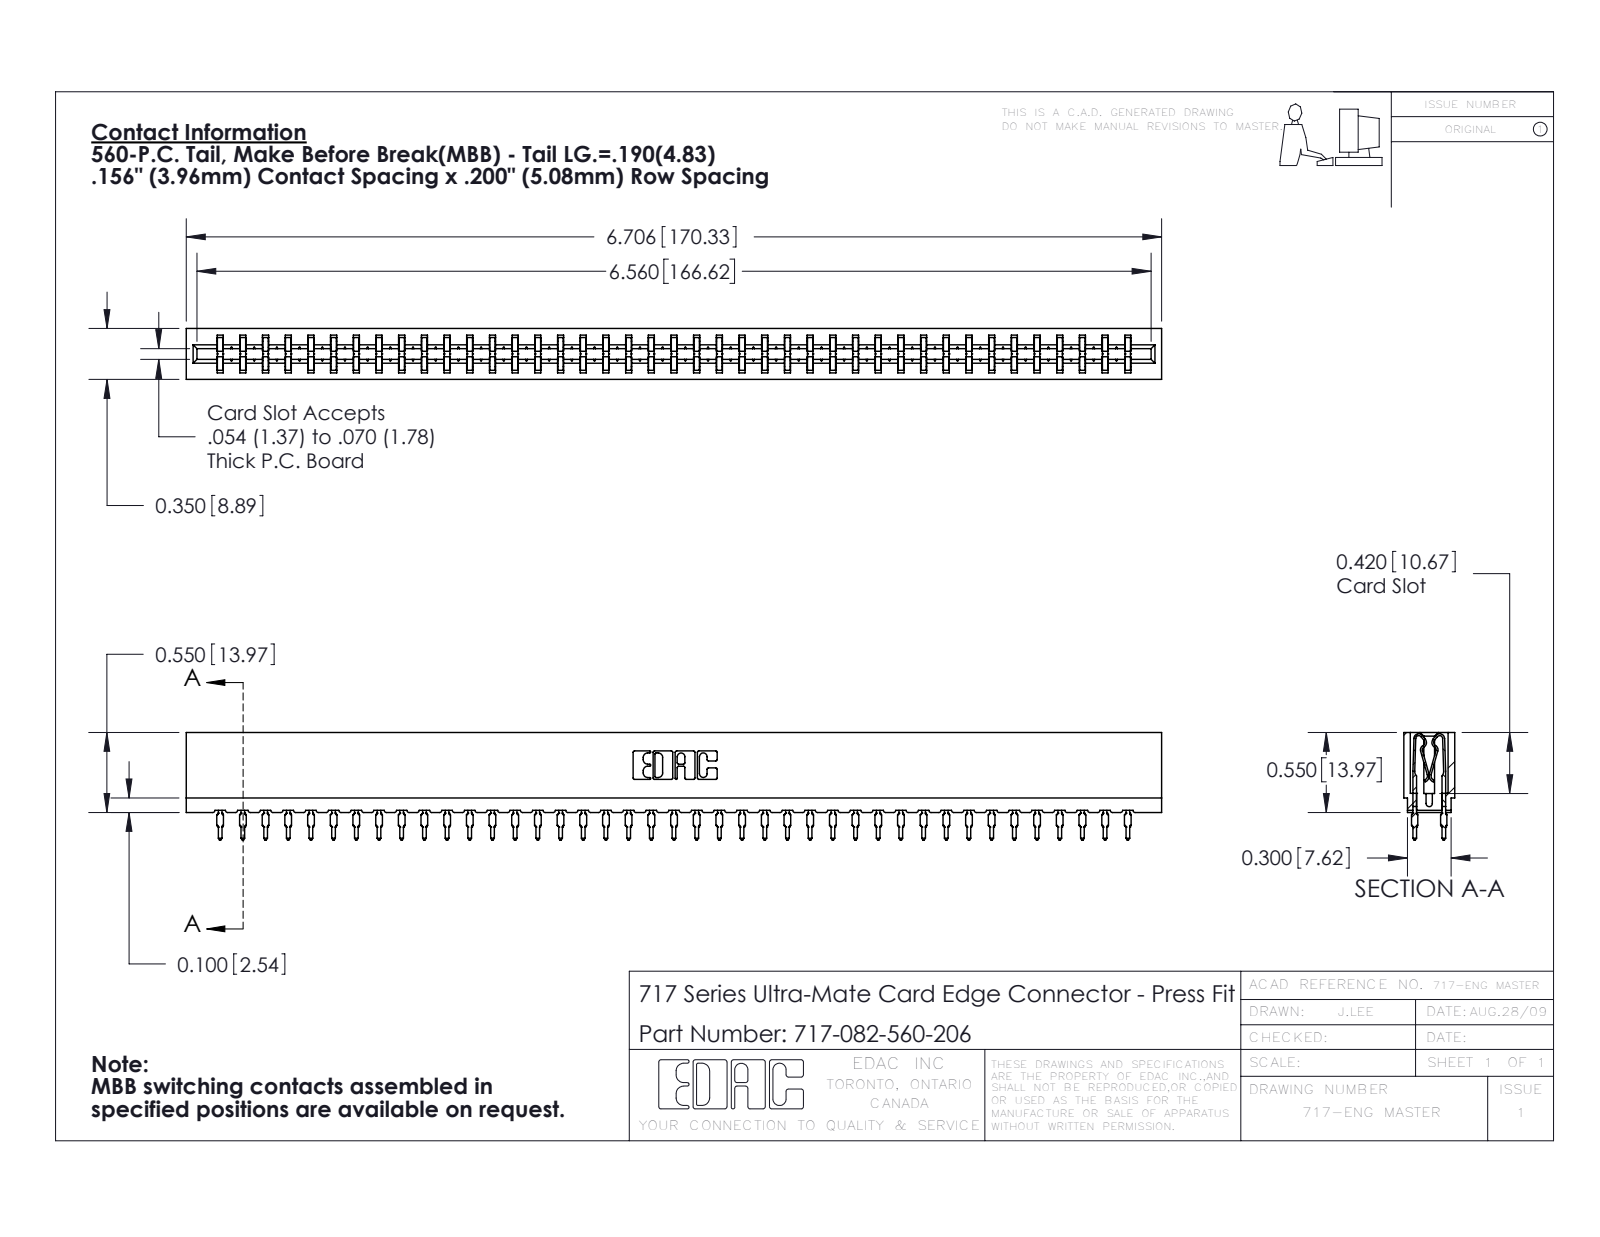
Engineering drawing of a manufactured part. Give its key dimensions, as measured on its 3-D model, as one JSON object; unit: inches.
{"part_name": "717 Part_Insulator Option - 06; 717-082-560-206; 745-292-001_560", "step_written_by": "SolidWorks 2016 (CONFIG_CONTROL_DESIGN)", "units": "inches", "bodies": {"solids": 83, "faces": 8212, "planar": 4277, "cylindrical": 1803, "other": 2132}, "overall_size": [6.706, 0.739, 0.35], "volume_in3": 0.919, "surface_area_in2": 37.94, "partial_cylinders_radius": [[0.021, 164], [0.015, 82], [0.01, 22], [0.005, 8], [0.011, 8], [0.007, 6], [0.031, 6], [0.026, 3]], "face_to_face_distances": [0.212, 0.138, 0.35, 0.063, 0.287, 0.076, 0.149, 0.074, 0.045, 0.305]}
